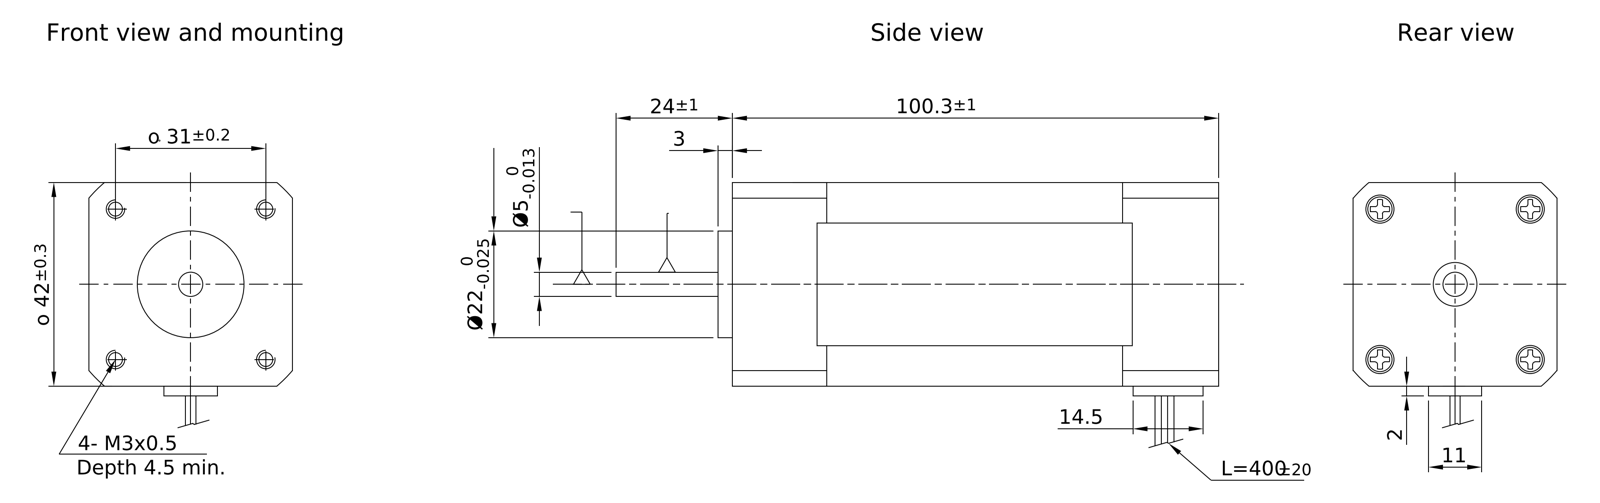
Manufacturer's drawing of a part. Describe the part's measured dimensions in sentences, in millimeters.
The part is named "DB41C024030-A". Its 3-D file was written by "Autodesk Inventor 2016 (AUTOMOTIVE_DESIGN)". It is 16 solids with 262 faces: 133 planar, 57 cylindrical and 72 other. Overall it measures 124.34 by 72 by 42 millimeters. Its volume is 169 852 cubic millimeters and its surface area 32 760 square millimeters. Round holes: 4 of diameter 2.46, 4 of diameter 2.7, 4 of diameter 5.8, 1 of diameter 5, 1 of diameter 6, 1 of diameter 9. Round bosses or shafts: 8 of diameter 1.5, 4 of diameter 2.5, 4 of diameter 2.27, 1 of diameter 22. Partial cylindrical surfaces (rounded edges, fillets, slot ends): 1 of radius 5.5, 1 of radius 24.5, 1 of radius 27.5. The main face-to-face distances are 42, 72.5, 90.3, 17.8, 10, 82.5, 100.3, 3, 85.5, 2. The hole center spacings are 21.92, 31, 43.84.
